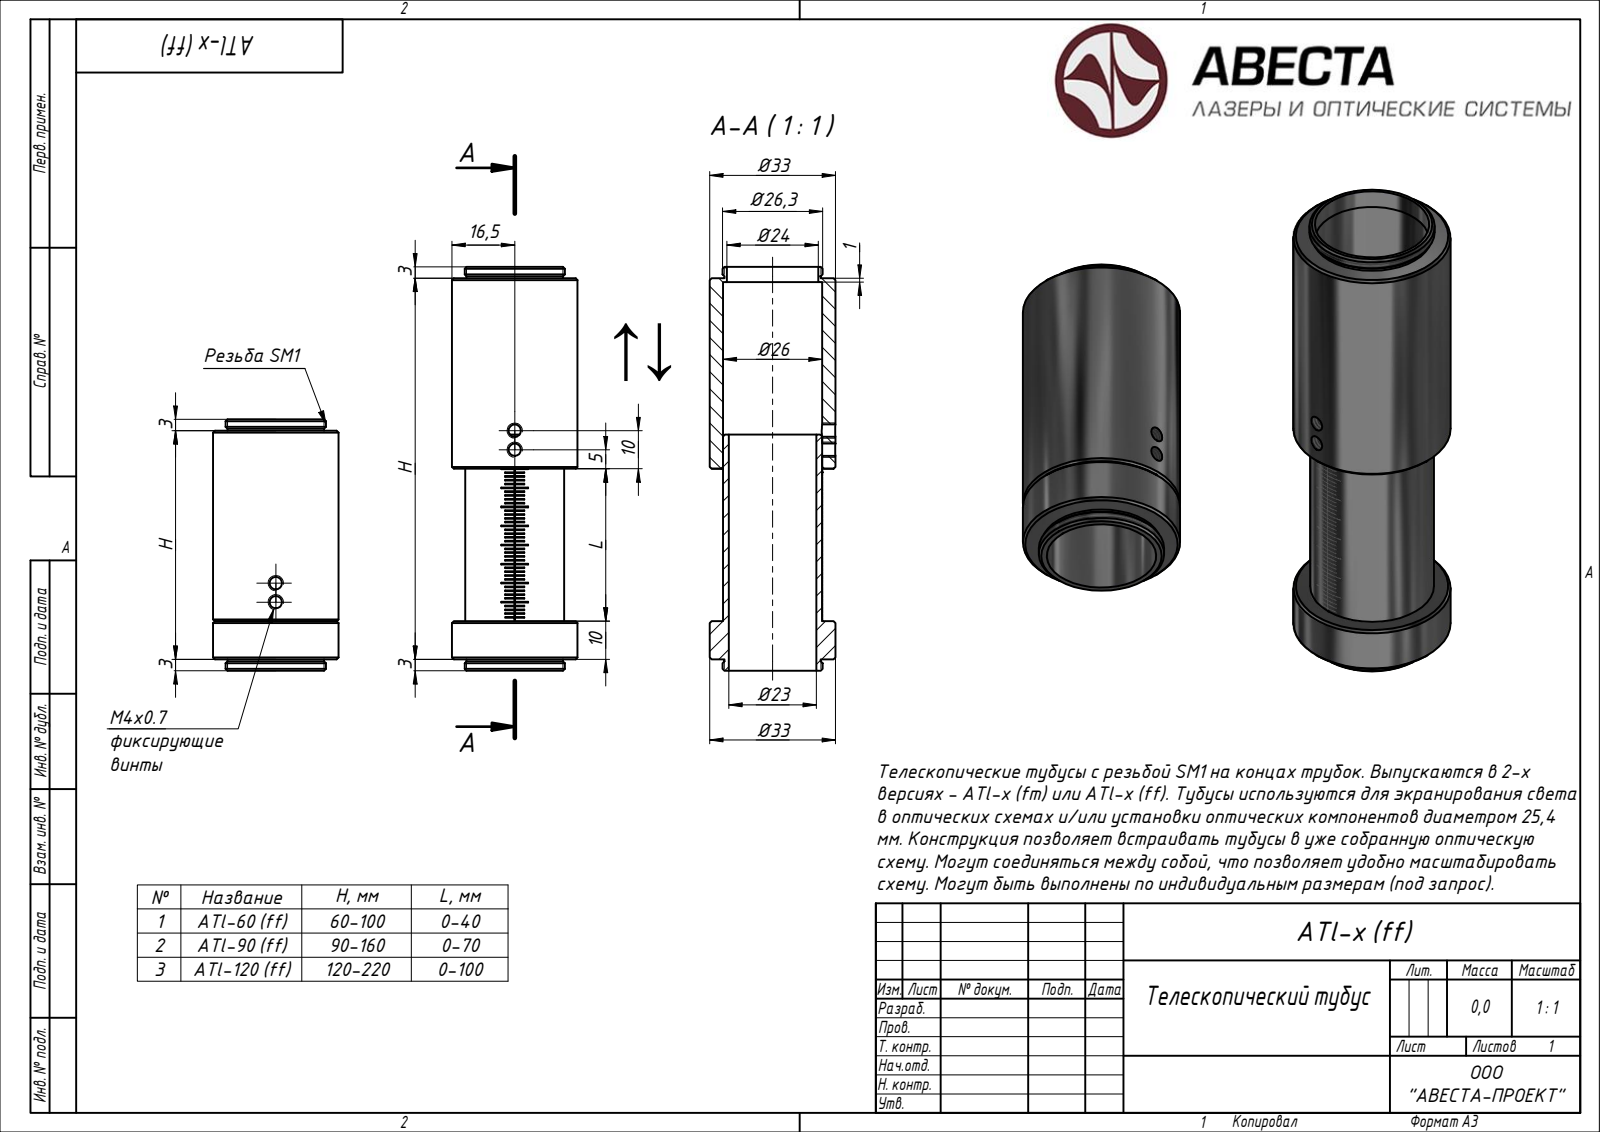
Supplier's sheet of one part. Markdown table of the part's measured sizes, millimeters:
| quantity | value |
| --- | --- |
| STEP written by | Rhino 7.34 (AUTOMOTIVE_DESIGN) |
| units | millimeters |
| bodies | 3 solids, 1854 faces (1710 planar, 84 cylindrical, 60 other) |
| overall size | 226 × 173 × 33 |
| volume | 119 738 mm³ |
| surface area | 90 015 mm² |
| round holes (diameter × count) | 3.24 × 6, 23 × 3, 24 × 3 |
| round bosses / shafts (diameter × count) | 33 × 3, 26.29 × 3, 26 × 3, 25.29 × 3 |
| partial cylindrical surfaces (radius × count) | 13 × 3, 13.5 × 3 |
| main face-to-face distances | 60, 10, 50, 110, 100, 30, 80, 120, 3, 40 |
| hole center spacings | 76.16, 5, 70, 74.33, 78.26, 152.32, 140, 150.42 |
